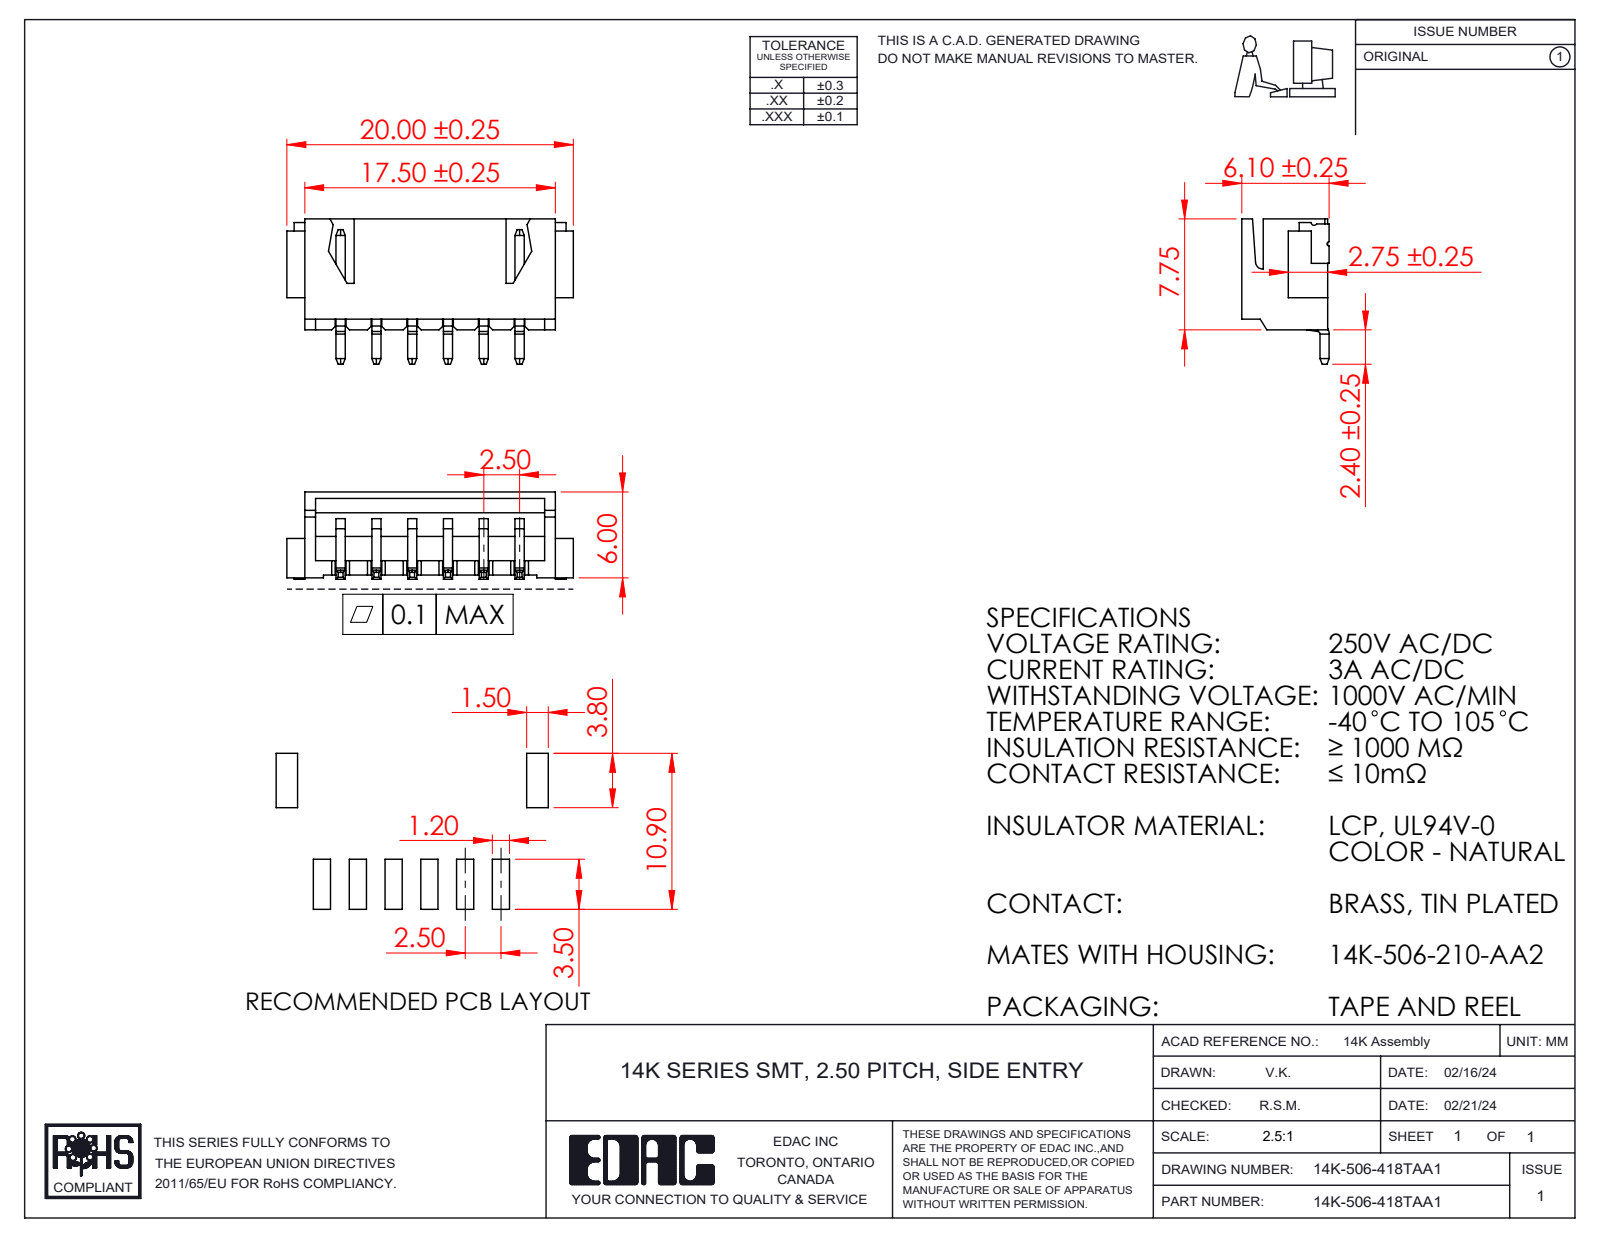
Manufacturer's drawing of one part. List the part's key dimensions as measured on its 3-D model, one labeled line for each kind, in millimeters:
Part name (STEP PRODUCT): 14K Series SMT Side Entry Insulator_506; 14K Series SMT Pin_Side Entry; 14K-506-418TAA1
STEP written by: SolidWorks 2023 (CONFIG_CONTROL_DESIGN)
Units: millimetres
Bodies: 7 solids, 397 faces (354 planar, 43 cylindrical, 0 other)
Overall size (bounding box): 20 × 10.15 × 6.1
Volume: 355 mm³ · Surface area: 1 109 mm²
Partial cylindrical surfaces — rounded edges, fillets, slot ends (radius × count): R0.38 ×12, R0.18 ×2, R0.82 ×2, R0.14 ×1, R0.2 ×1, R0.5 ×1
Main face-to-face distances: 0.75, 5.05, 2.5, 5.8, 0.64, 4.3, 1.86, 5, 0.5, 1.24
